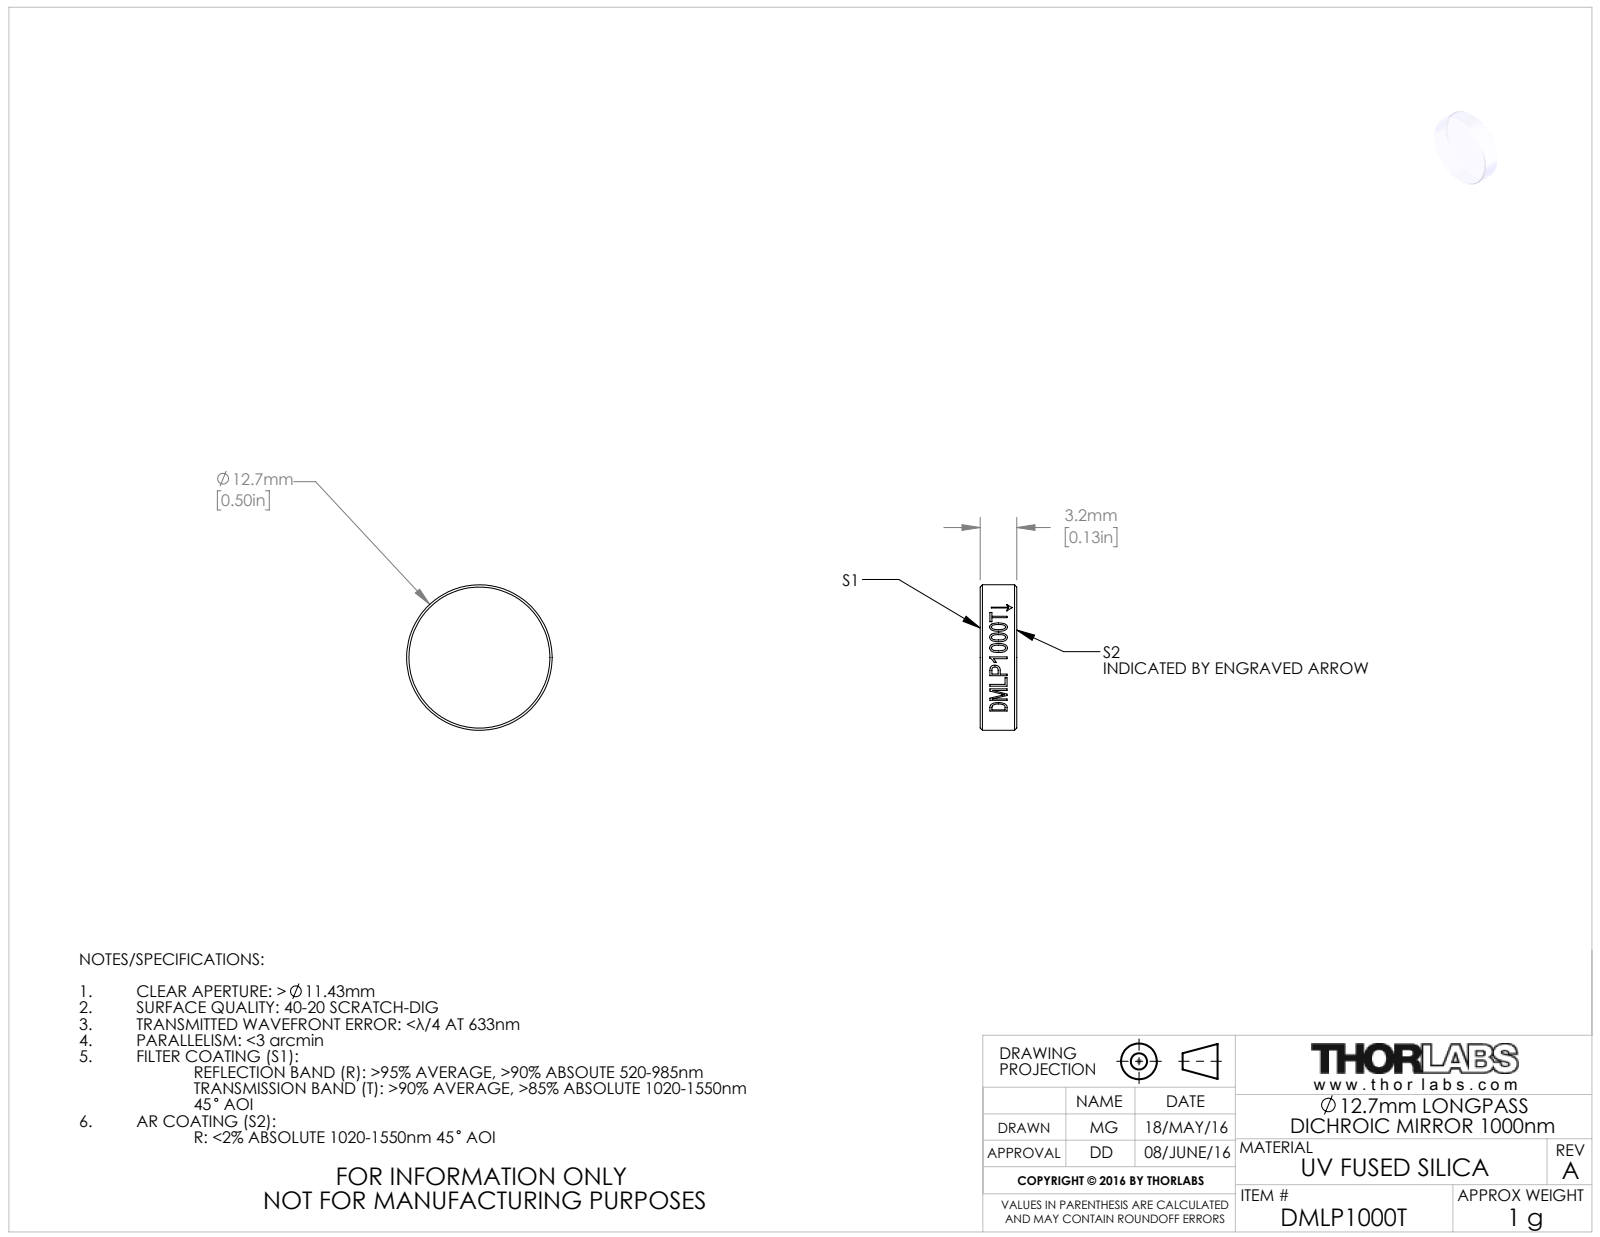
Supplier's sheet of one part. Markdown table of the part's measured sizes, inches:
| quantity | value |
| --- | --- |
| part name | TTN045295-E0W |
| STEP written by | SolidWorks 2016 (CONFIG_CONTROL_DESIGN) |
| units | inches |
| bodies | 1 solid, 23 faces (2 planar, 17 cylindrical, 4 other) |
| overall size | 0.5 × 0.5 × 0.126 |
| volume | 0.025 in³ |
| surface area | 0.575 in² |
| round bosses / shafts (diameter × count) | 0.5 × 1 |
| main face-to-face distances | 0.126 |
